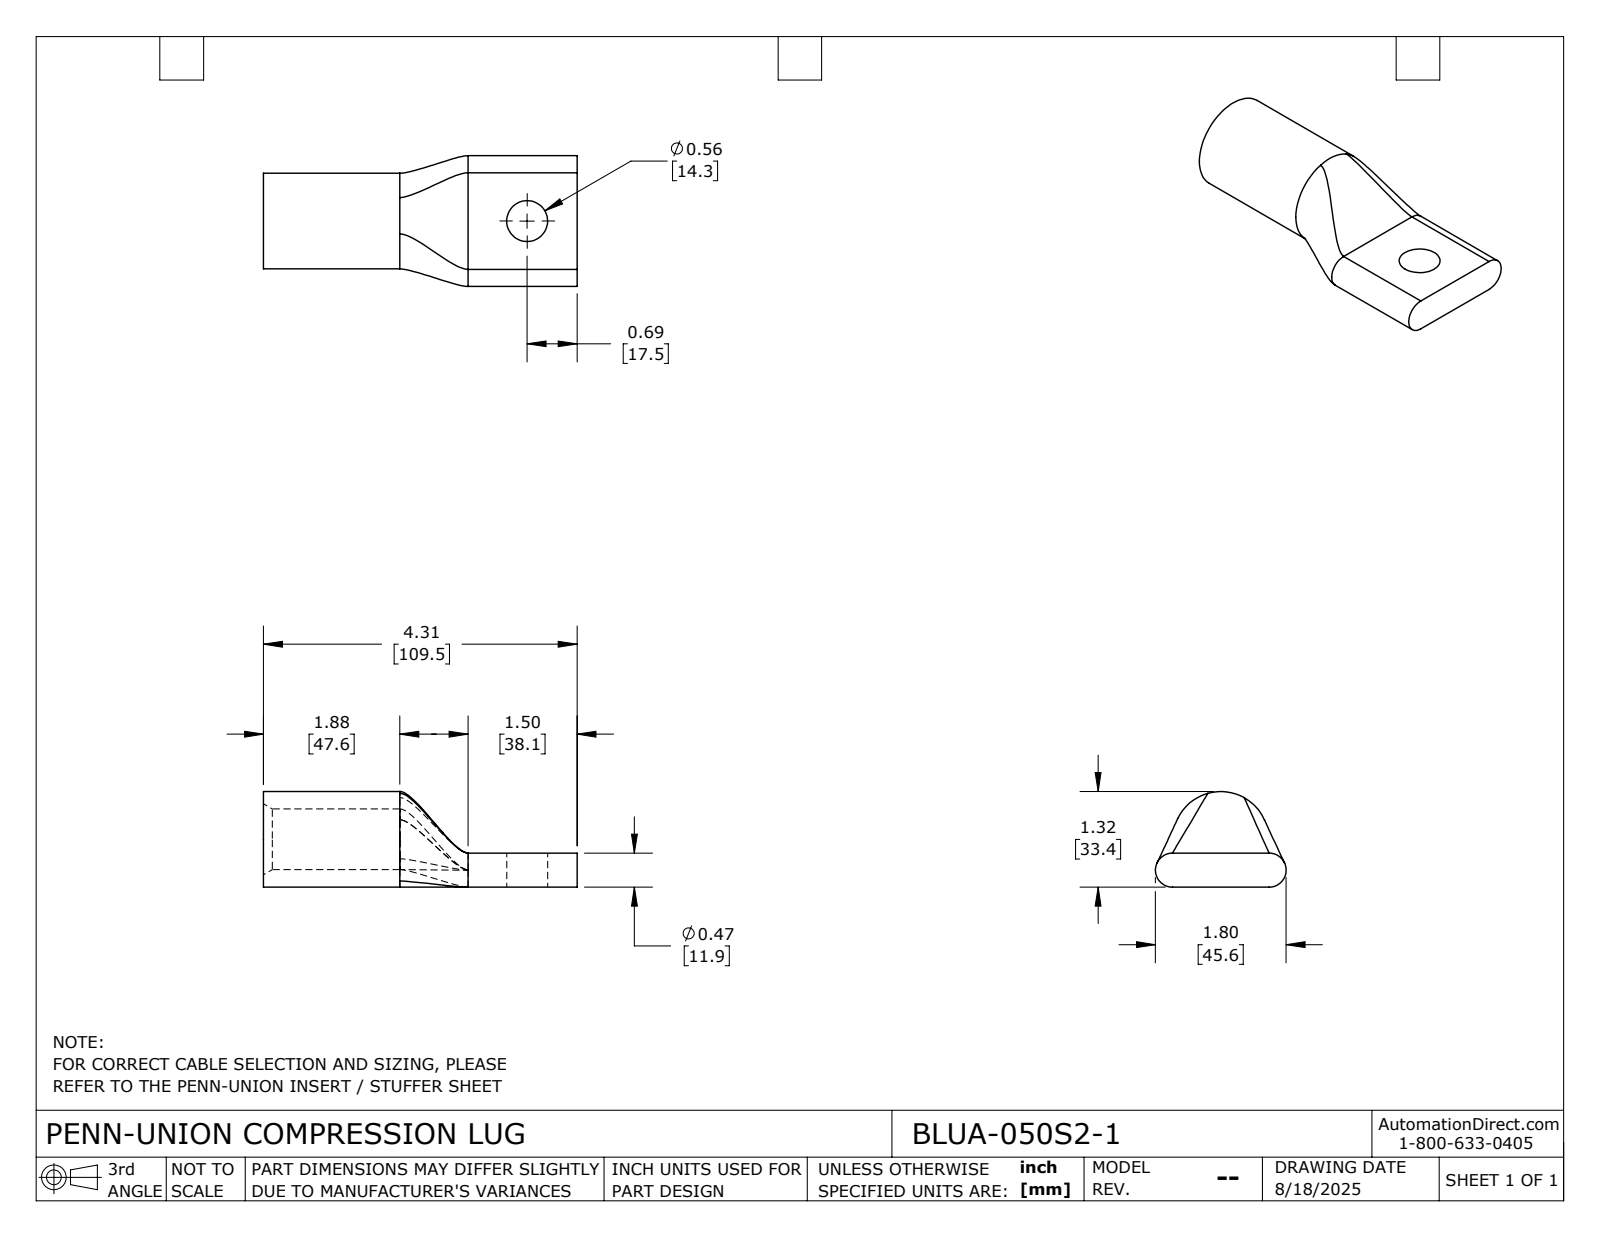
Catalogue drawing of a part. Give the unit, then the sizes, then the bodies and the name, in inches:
Units: inches
Overall size (bounding box): 4.313 × 1.797 × 1.315
Round holes (diameter × count): ⌀0.563 ×1, ⌀0.834 ×1
Round bosses / shafts (diameter × count): ⌀1.315 ×1
Partial cylindrical surfaces — rounded edges, fillets, slot ends (radius × count): R0.234 ×2
Main face-to-face distances: 0.469, 4.313, 2.813, 1.5
Volume: 3.335 in³ · Surface area: 27.69 in²
Bodies: 1 solid, 24 faces (5 planar, 9 cylindrical, 10 other)
Part name (STEP PRODUCT): BLUA-050S2-1
STEP written by: SolidWorks 2024 (CONFIG_CONTROL_DESIGN)
